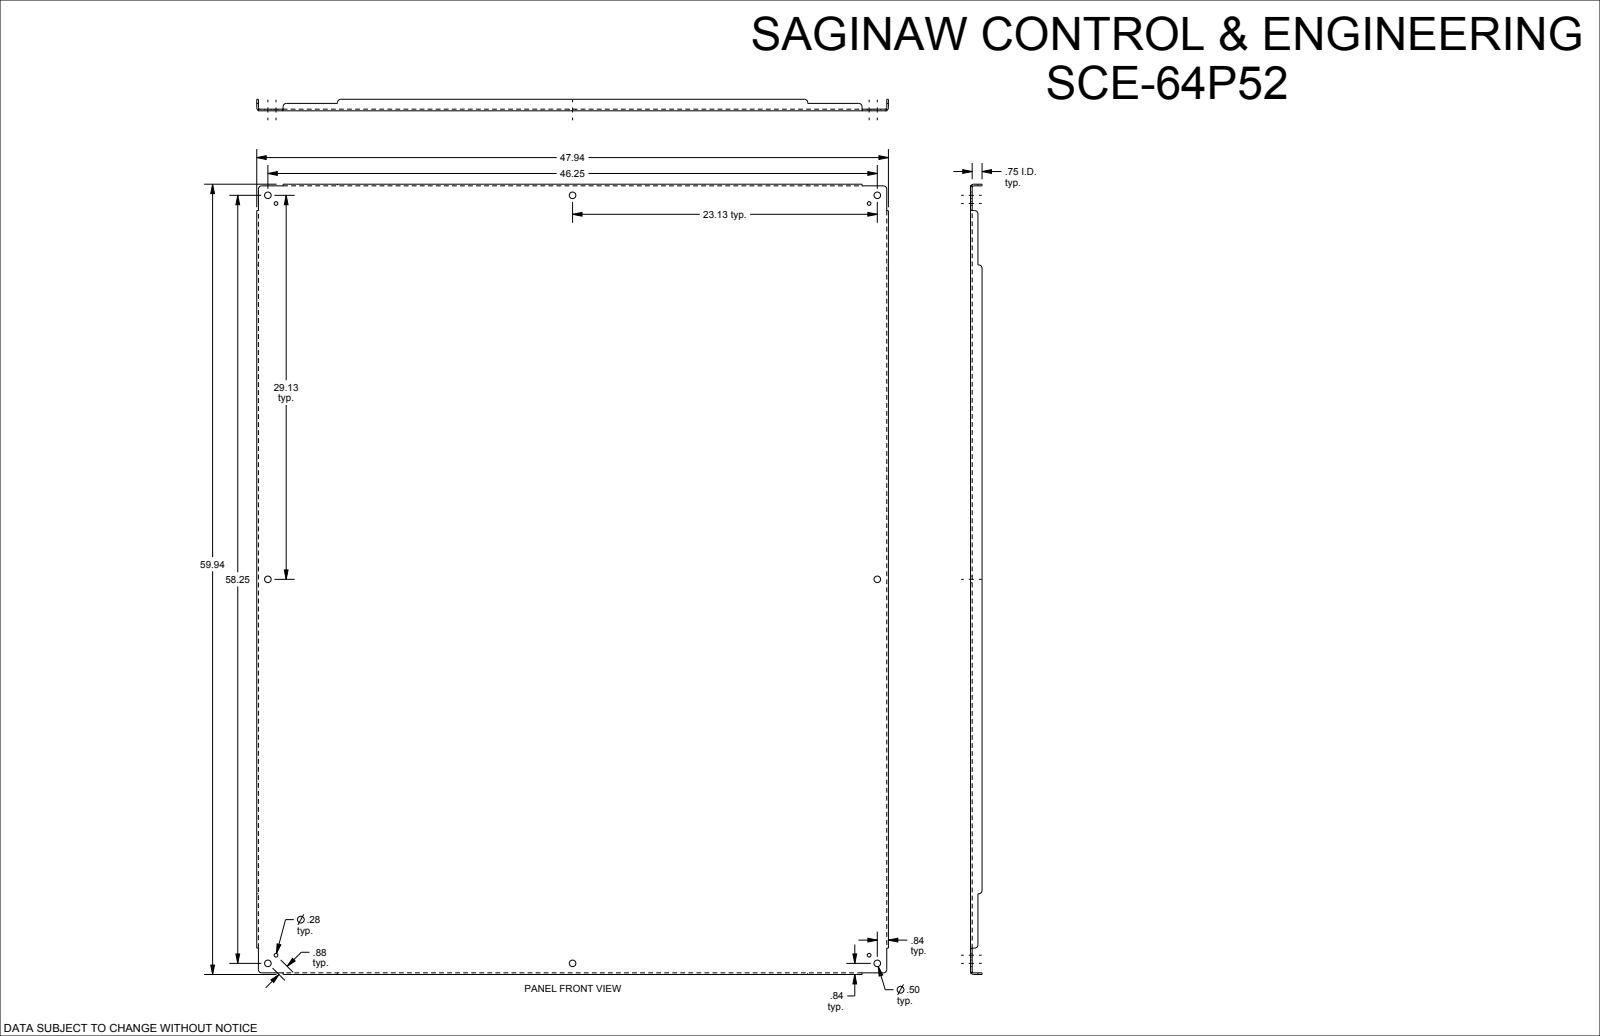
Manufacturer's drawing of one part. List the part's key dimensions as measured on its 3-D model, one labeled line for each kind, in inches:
Part name (STEP PRODUCT): SCE-64P52
STEP written by: SolidWorks 2019 (CONFIG_CONTROL_DESIGN)
Units: inches
Bodies: 1 solid, 110 faces (46 planar, 40 cylindrical, 24 other)
Overall size (bounding box): 59.938 × 47.938 × 0.875
Volume: 374.2 in³ · Surface area: 6 017 in²
Round holes (diameter × count): ⌀0.5 ×8, ⌀0.281 ×4
Partial cylindrical surfaces — rounded edges, fillets, slot ends (radius × count): R0.25 ×12, R0.112 ×4, R0.237 ×4
Main face-to-face distances: 0.125, 0.125, 47.813, 59.813, 47.687, 47.938, 59.687, 59.938, 0.75, 0.875
Hole centre spacings: 0.875, 22.515, 23.125, 28.513, 29.125, 37.189, 45.636, 53.804
